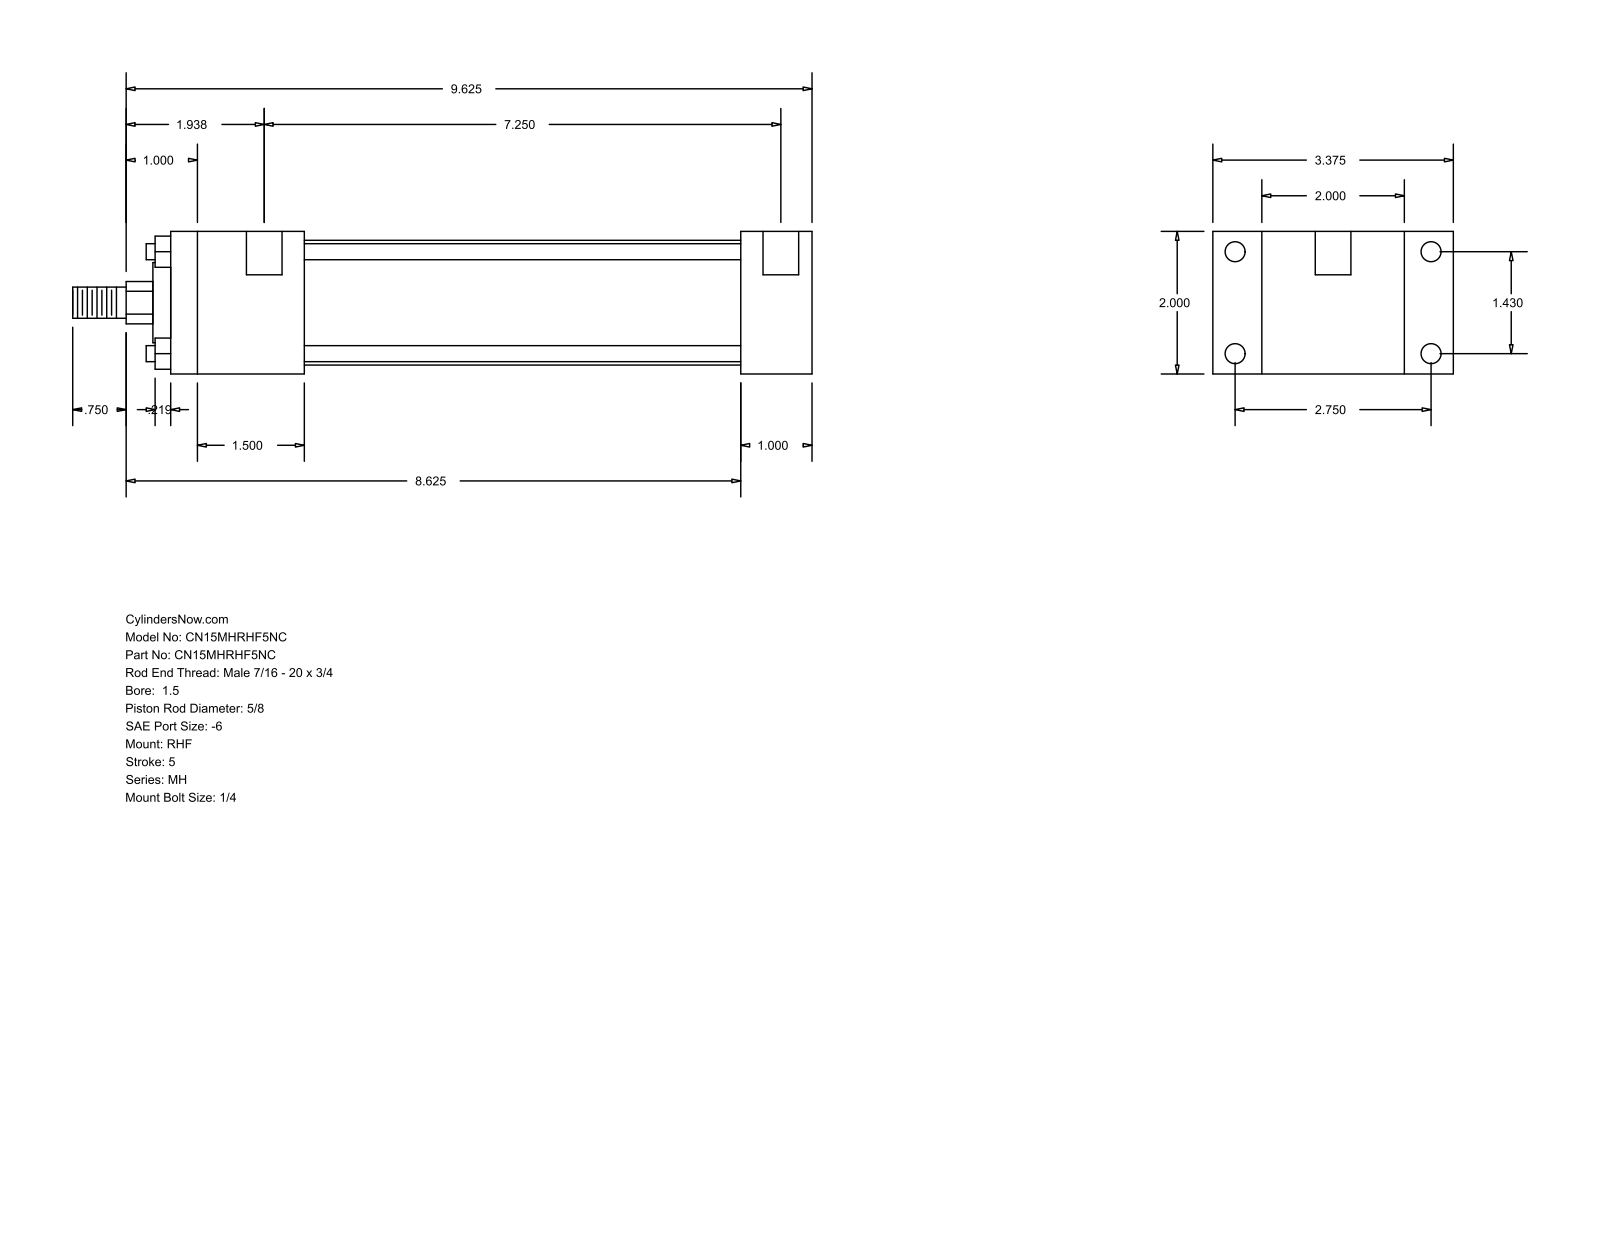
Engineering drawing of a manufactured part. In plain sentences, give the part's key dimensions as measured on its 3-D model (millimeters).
The part is named "MH_RHF__0150_0.625". Its 3-D file was written by "GSSL Pune (CONFIG_CONTROL_DESIGN)". It is 0 solids with 88 faces: 60 planar, 28 cylindrical and 0 other. Overall it measures 263.52 by 85.72 by 50.8 millimeters. Round holes: 4 of diameter 5.56, 4 of diameter 7.14, 2 of diameter 12.7. Round bosses or shafts: 4 of diameter 5.71, 1 of diameter 44.45, 1 of diameter 28.57, 1 of diameter 15.88, 1 of diameter 11.11. Partial cylindrical surfaces (rounded edges, fillets, slot ends): 1 of radius 7.54. The main face-to-face distances are 50.8, 25.4, 17.46, 68.26, 203.19, 228.59, 85.72, 47.62, 155.57, 180.97. The hole center spacings are 36.32, 69.84, 78.72, 187.32, 3.17, 184.15.
